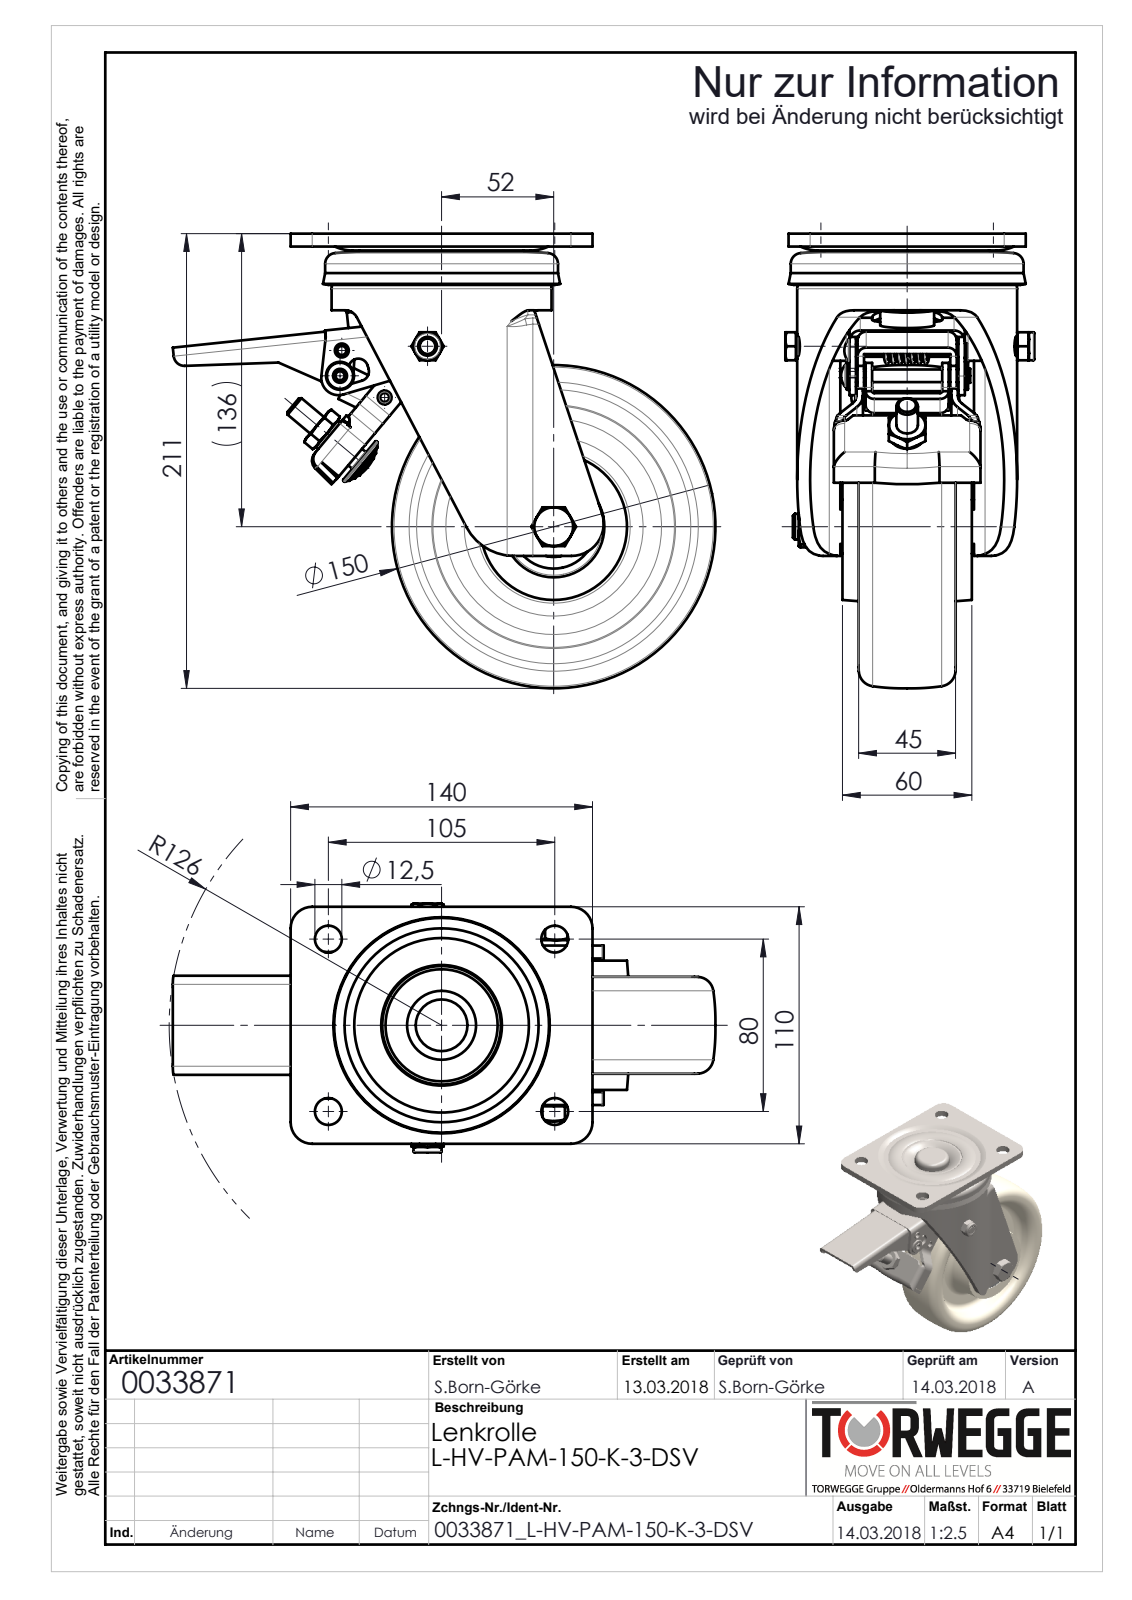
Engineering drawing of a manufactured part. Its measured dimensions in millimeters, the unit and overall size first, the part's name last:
Units: millimetres
Overall size (bounding box): 251.66 × 211.02 × 115.5
Round holes (diameter × count): ⌀6.2 ×3, ⌀5.85 ×2, ⌀6.5 ×2, ⌀10.1 ×2, ⌀13 ×2, ⌀20 ×2, ⌀4.2 ×1, ⌀6.15 ×1, ⌀8.2 ×1, ⌀9.2 ×1, ⌀10.2 ×1, ⌀12 ×1
Round bosses / shafts (diameter × count): ⌀12.5 ×4, ⌀4.2 ×2, ⌀103 ×1, ⌀102 ×1, ⌀65.61 ×1, ⌀32 ×1, ⌀28.1 ×1, ⌀25 ×1
Partial cylindrical surfaces — rounded edges, fillets, slot ends (radius × count): R1 ×13, R5 ×12, R10 ×9, R1.5 ×8, R2.5 ×8, R6 ×5, R15 ×5, R4 ×4
Main face-to-face distances: 6, 3, 7, 60, 25, 1, 61, 67, 68, 35
Hole centre spacings: 23.01, 11.78, 29.5, 29.51, 31, 31.02, 39.82, 42.84
Bodies: 0 solids, 709 faces (273 planar, 207 cylindrical, 229 other)
Part name (STEP PRODUCT): 0033871_L-HV-PAM-150-K-3-DSV
STEP written by: SolidWorks 2018 (AUTOMOTIVE_DESIGN)
